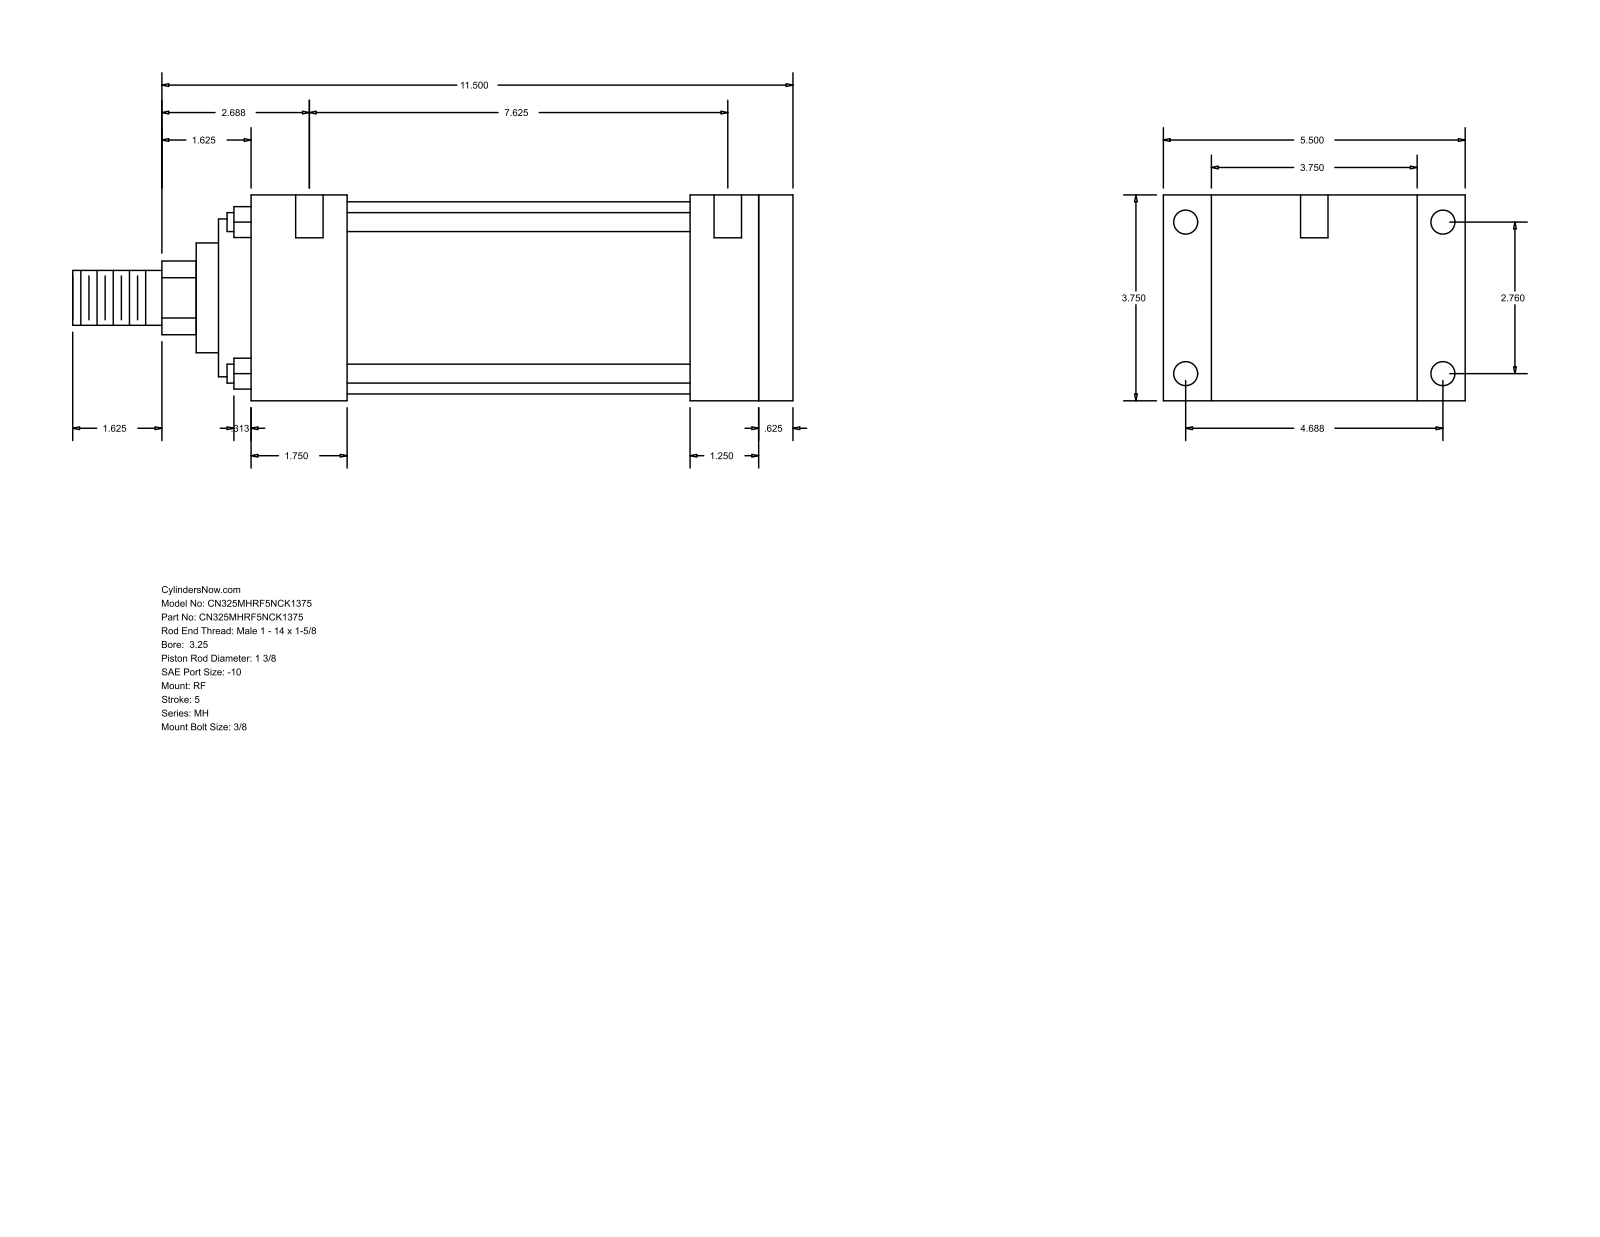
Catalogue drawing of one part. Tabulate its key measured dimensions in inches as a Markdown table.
| quantity | value |
| --- | --- |
| part name | MH_RF__0325_1.375 |
| STEP written by | GSSL Pune (CONFIG_CONTROL_DESIGN) |
| units | inches |
| bodies | 0 solids, 94 faces (65 planar, 29 cylindrical, 0 other) |
| overall size | 13.125 × 5.5 × 3.75 |
| round holes (diameter × count) | 0.219 × 4, 0.438 × 4, 0.5 × 2 |
| round bosses / shafts (diameter × count) | 0.345 × 4, 3.5 × 1, 2.875 × 1, 2 × 1, 1.375 × 1, 1 × 1 |
| partial cylindrical surfaces (radius × count) | 0.672 × 1 |
| main face-to-face distances | 3.75, 9.875, 9.25, 0.625, 0.875, 4.625, 1.75, 7.5, 8.125, 8 |
| hole center spacings | 2.76, 4.687, 5.439, 7.875, 0.063, 0.187, 7.625, 7.688 |
